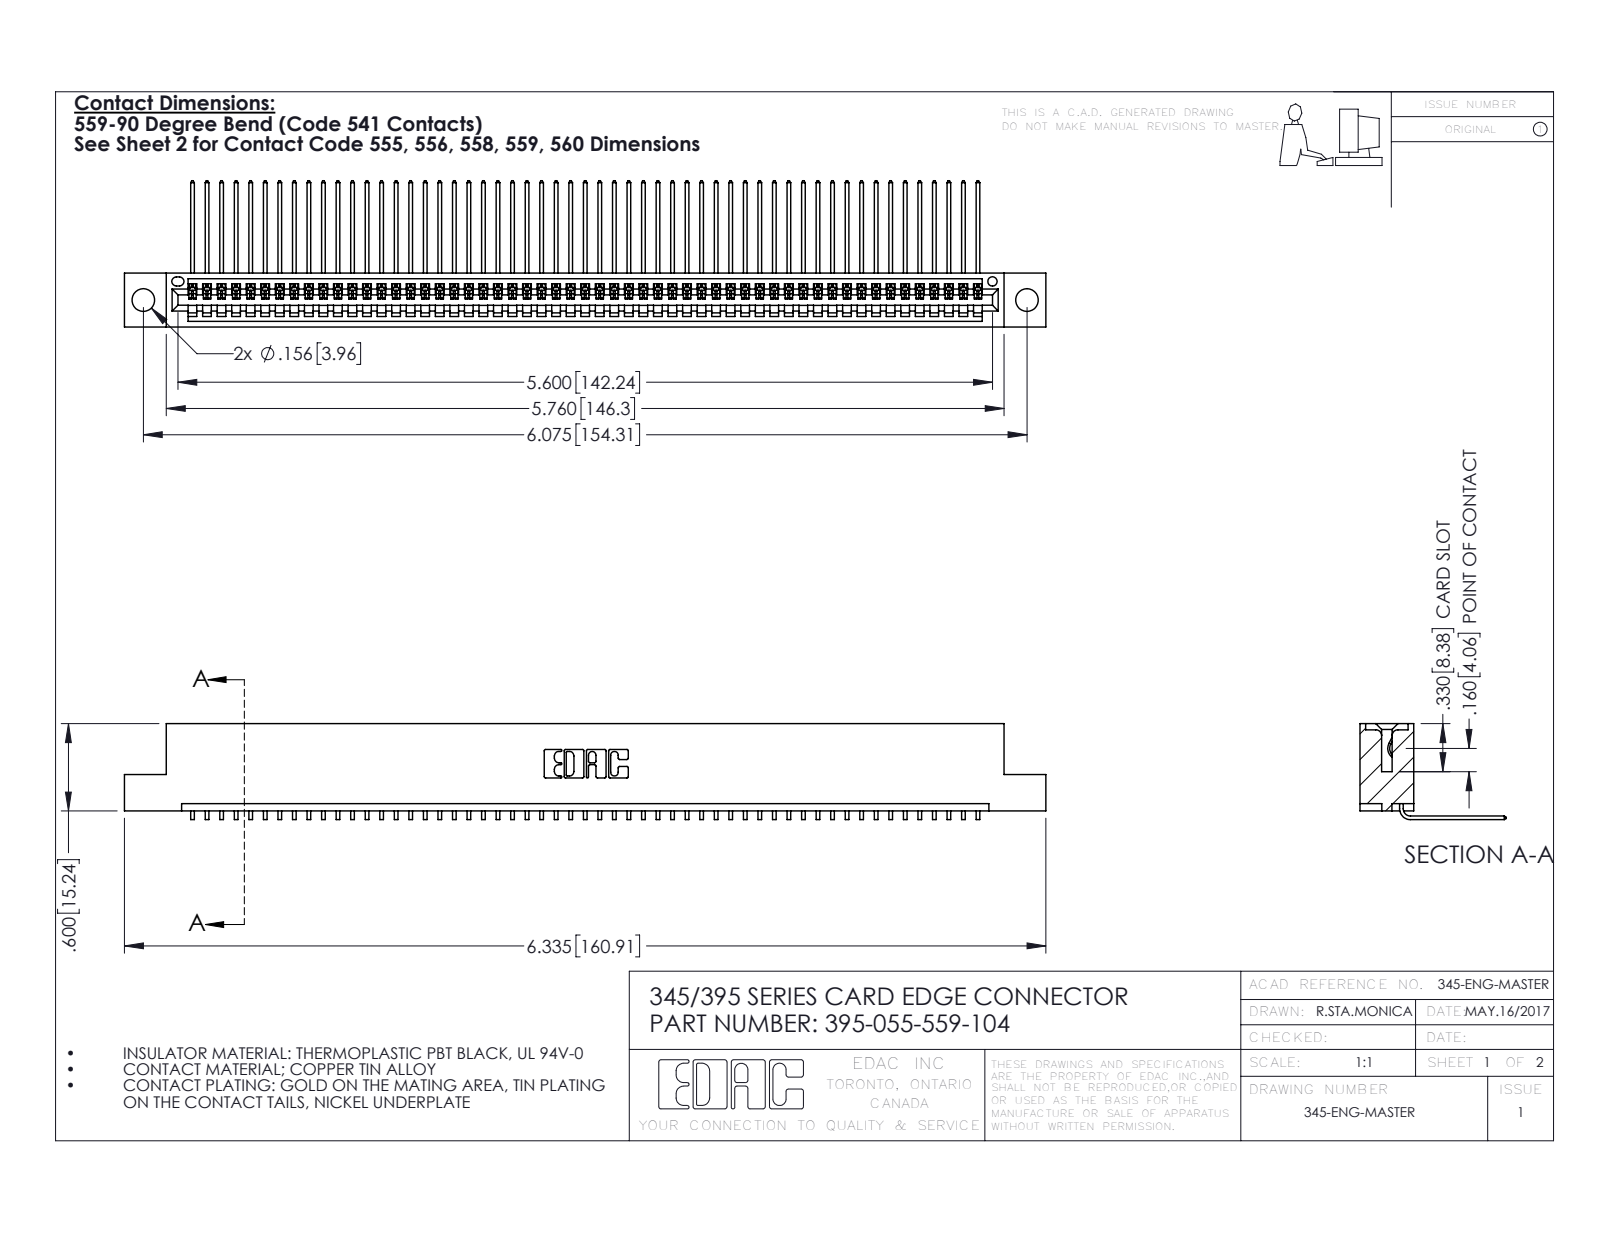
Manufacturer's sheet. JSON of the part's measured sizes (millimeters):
{"part_name": "395-055-559-104; 345-292-001_558 559 Tail - 1; 345 Part_Flush Mounting Lugs - 0.156 Dia-TH", "step_written_by": "SolidWorks 2016 (CONFIG_CONTROL_DESIGN)", "units": "millimeters", "bodies": {"solids": 56, "faces": 3426, "planar": 2390, "cylindrical": 1036, "other": 0}, "overall_size": [160.9, 25.5, 16.7], "volume_mm3": 15500, "surface_area_mm2": 21640, "round_holes": [[4, 2], [1.6, 1]], "partial_cylinders_radius": [[0.2, 110], [0.3, 22], [0.2, 6], [0.8, 6], [0.7, 3], [0.8, 2], [1, 2], [0.4, 1]], "face_to_face_distances": [7.6, 1.8, 9.4, 5.1, 2.5, 6.9, 0.6, 5.7, 3.8, 1.8], "hole_center_spacings": [6.9, 148.3, 154.3]}
